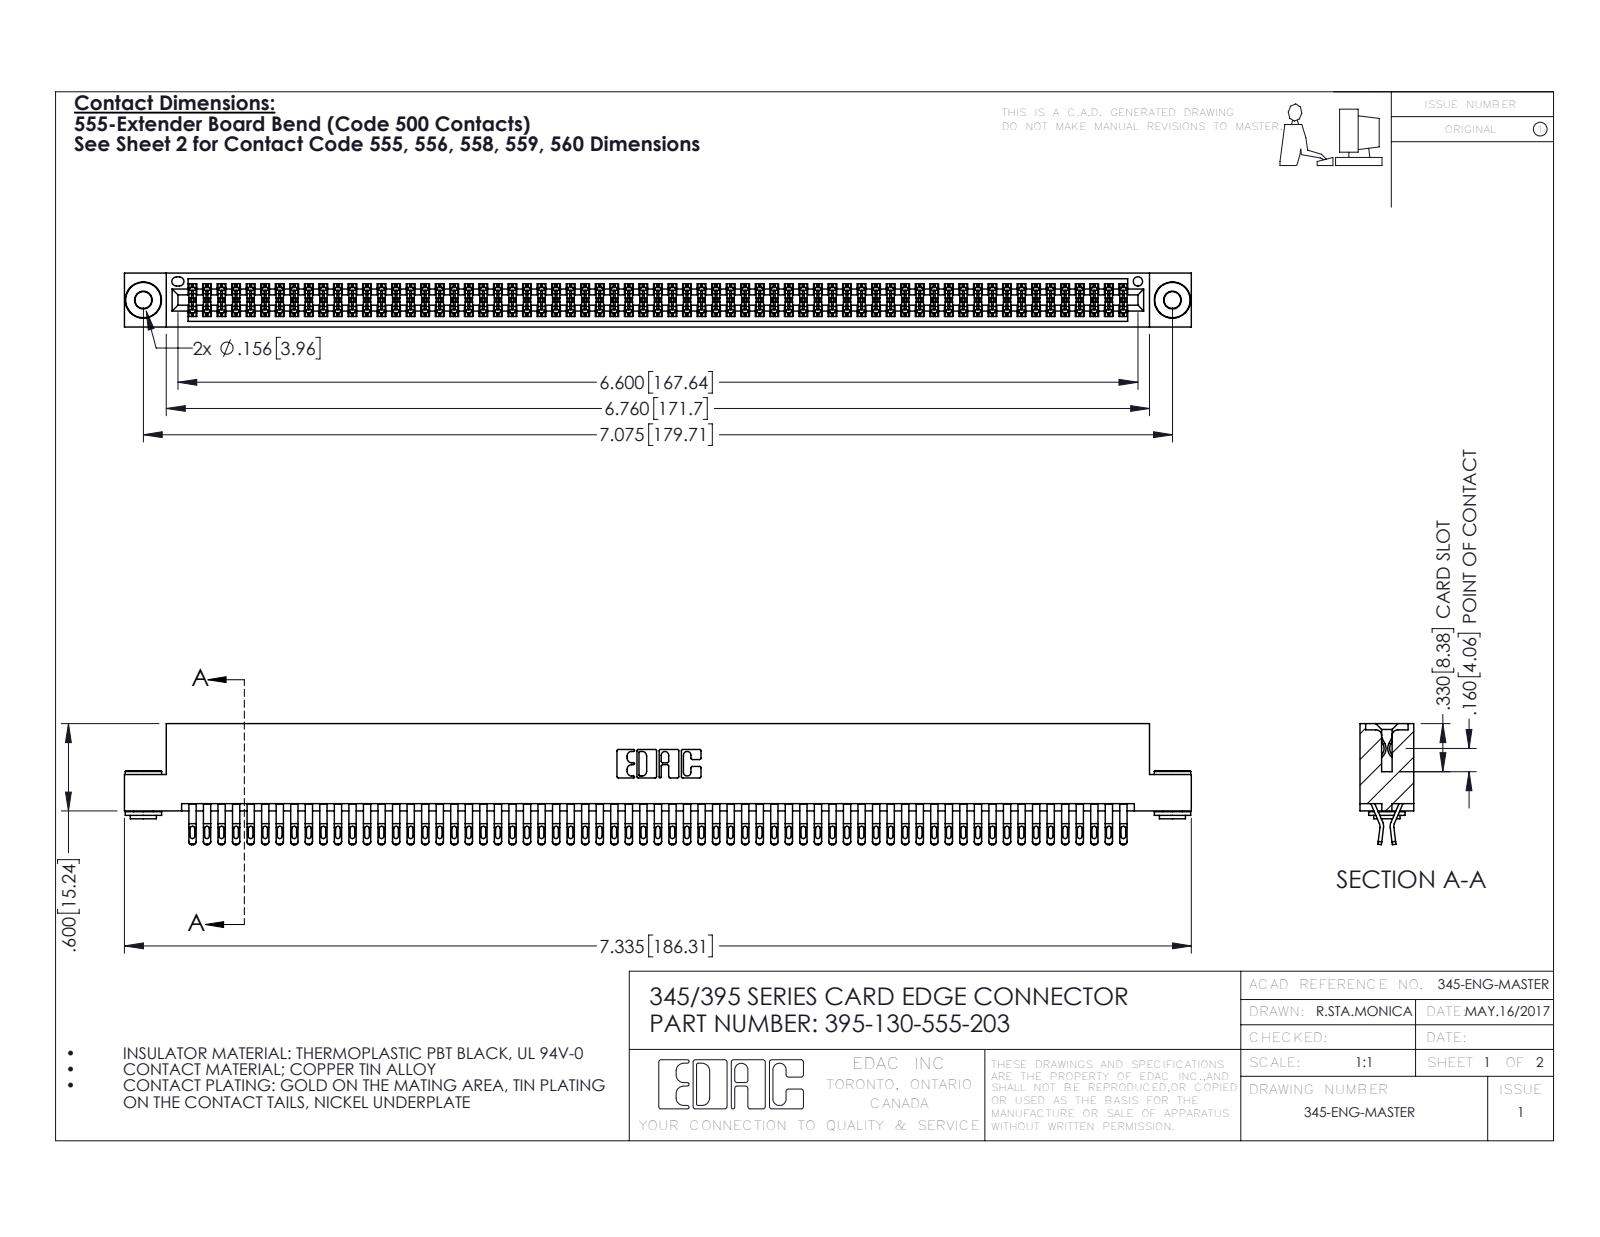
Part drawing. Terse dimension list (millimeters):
name: 345-250-002_345-250-002-102; 345-292-001_555 Tail; 395-130-555-203; 345 Part_Flush Mounting Lugs - 0.156 Dia-TH
written by: SolidWorks 2016 (CONFIG_CONTROL_DESIGN)
unit: mm
bodies: 133 solids, 7444 faces (4120 planar, 3316 cylindrical, 8 other)
size: 186.3 × 21.1 × 9.4
volume: 18 710 mm³; area: 29 610 mm²
holes: 2× ⌀2.9, 2× ⌀4, 1× ⌀1.6
bosses: 2× ⌀6.4, 2× ⌀4.6, 2× ⌀3.5
rounds: 325× R0.4, 260× R0.5, 195× R0.2, 22× R0.3, 6× R0.2, 6× R0.8, 3× R0.7, 2× R0.3
face distances: 1.8, 7.6, 0.6, 5.1, 9.4, 2.5, 6.9, 5.7, 4.4, 3.8
hole spacings: 6.9, 173.7, 179.7
